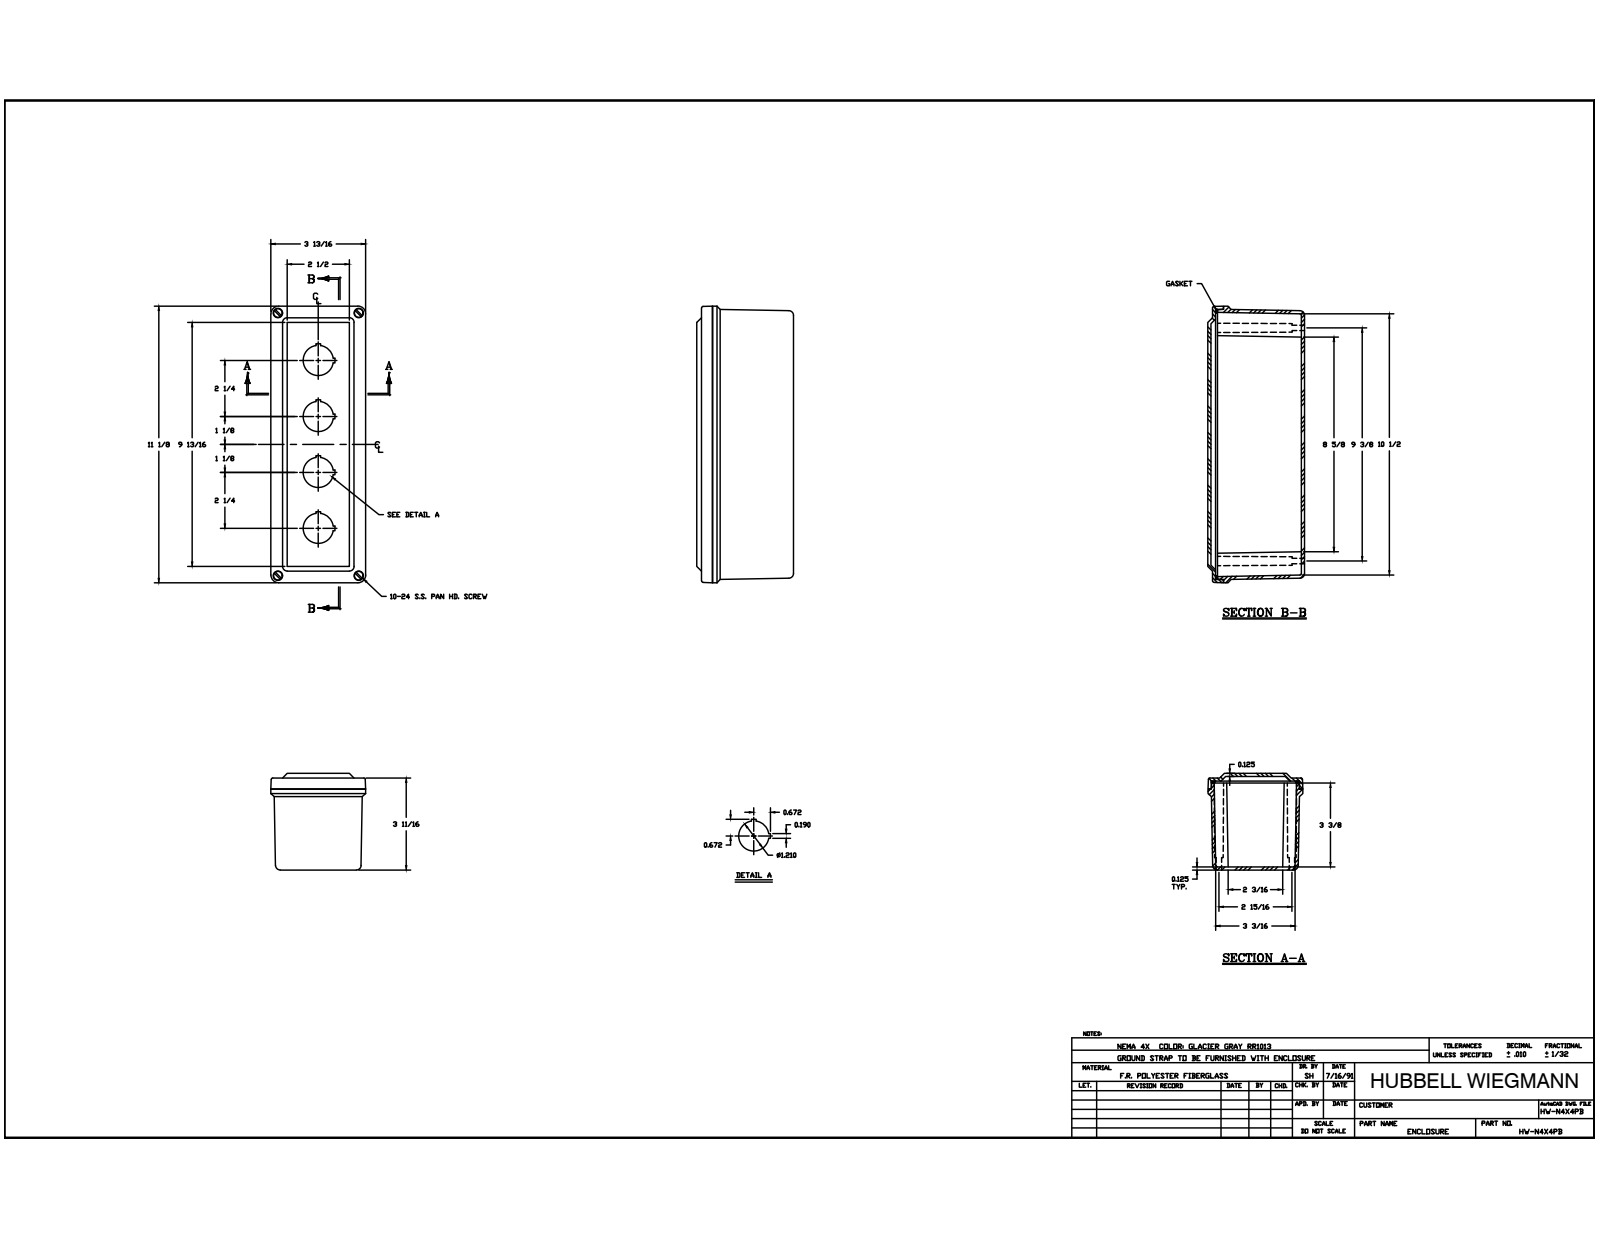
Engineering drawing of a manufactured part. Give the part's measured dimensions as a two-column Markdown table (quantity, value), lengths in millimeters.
| quantity | value |
| --- | --- |
| part name | WPCF1144 BOX; 10-24 X 0.4375 DP BRASS INSERT; WPCF4PB CVR; WPCF1144 GASKET (+3 more) |
| STEP written by | Autodesk Inventor 2014 (AUTOMOTIVE_DESIGN) |
| units | millimeters |
| bodies | 11 solids, 411 faces (207 planar, 112 cylindrical, 92 other) |
| overall size | 282.57 × 98.42 × 96.84 |
| volume | 471 224 mm³ |
| surface area | 257 548 mm² |
| round holes (diameter × count) | 5.56 × 8, 3.68 × 4, 4.83 × 4, 9.52 × 4, 30.73 × 4 |
| round bosses / shafts (diameter × count) | 9.42 × 4, 5.54 × 4, 4.5 × 4 |
| partial cylindrical surfaces (radius × count) | 0.79 × 20, 0.3 × 16, 7.94 × 8, 1.59 × 4, 4.47 × 4, 4.76 × 4, 5.59 × 4, 8.26 × 4 |
| main face-to-face distances | 3.17, 3.42, 95.25, 4.76, 90.49, 98.42, 92.08, 12.7, 1.59, 87.32 |
| hole center spacings | 15.59, 50.04, 63.62, 80.01, 97.88, 113.35, 152.27, 167.86 |
